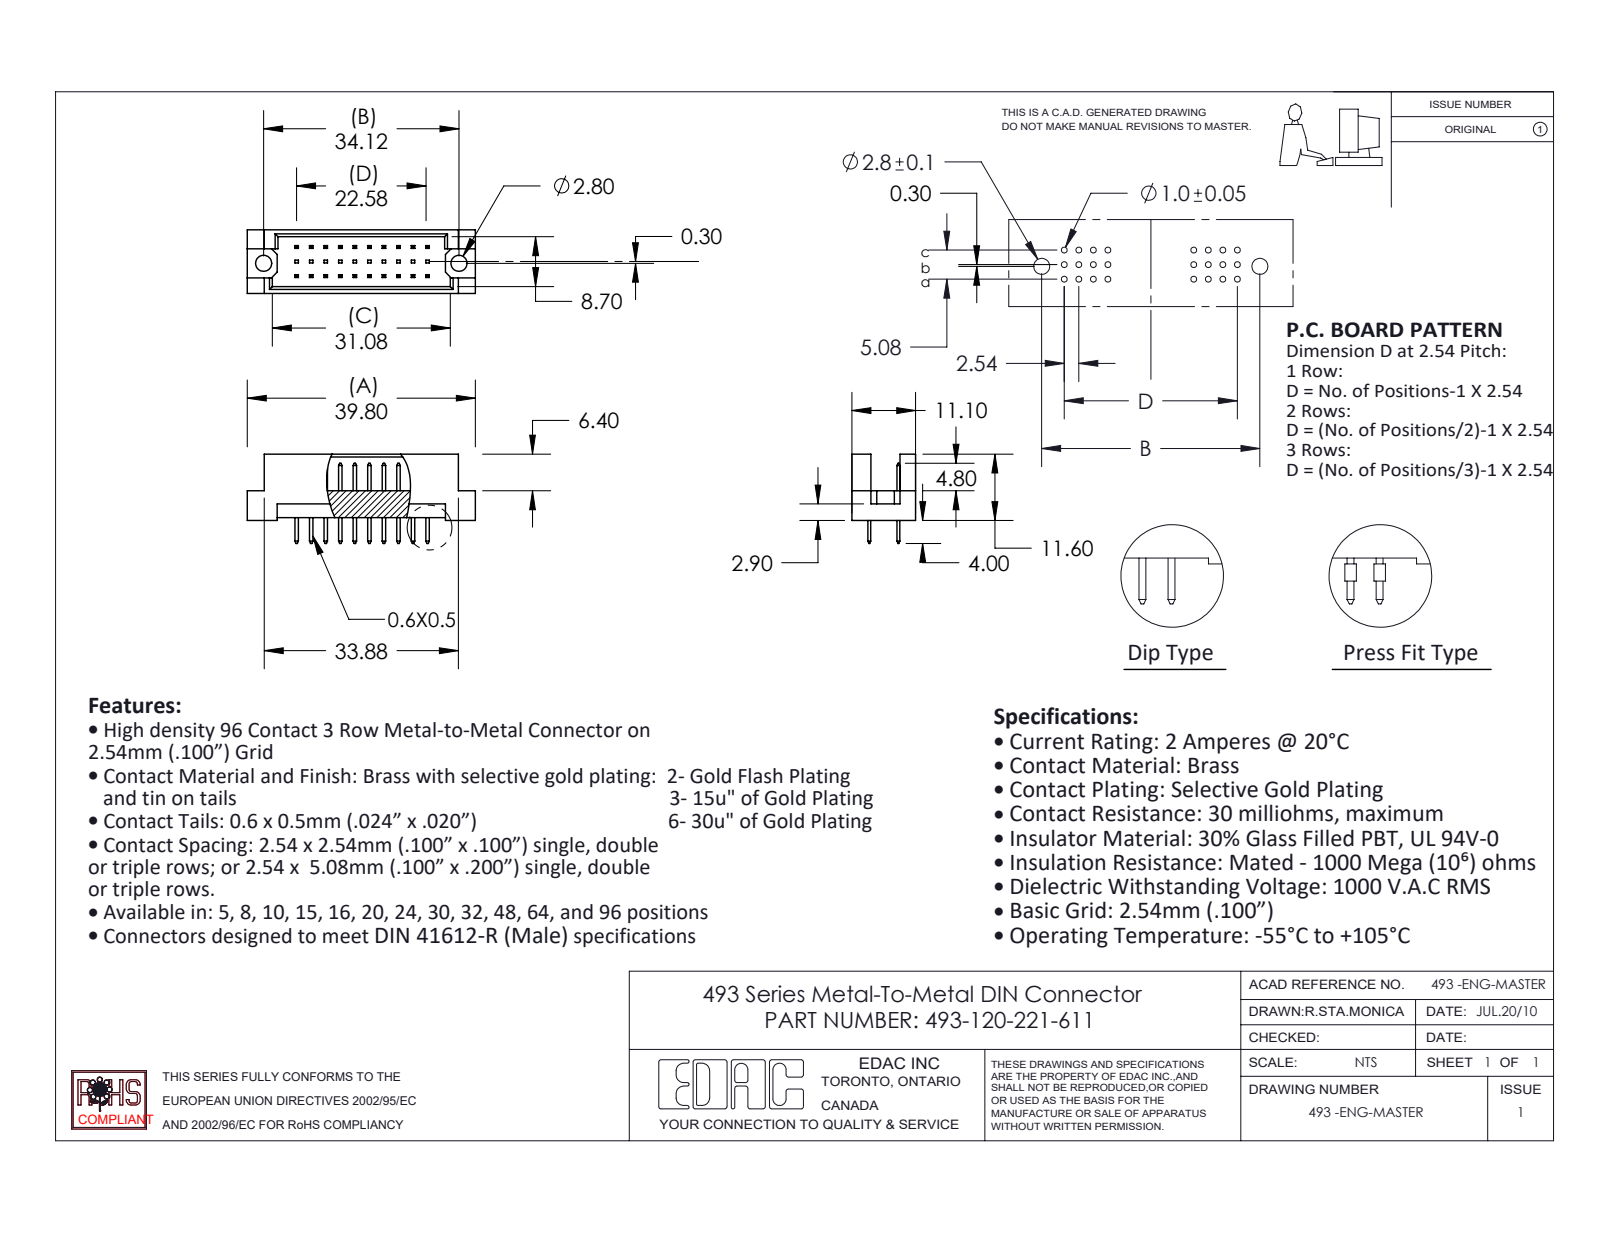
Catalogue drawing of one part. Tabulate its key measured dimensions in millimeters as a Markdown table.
| quantity | value |
| --- | --- |
| part name | 493 Part_30; 493-124-221-321; 493-290_21 |
| STEP written by | SolidWorks 2020 (CONFIG_CONTROL_DESIGN) |
| units | millimeters |
| bodies | 21 solids, 452 faces (448 planar, 4 cylindrical, 0 other) |
| overall size | 39.8 × 15.6 × 11.1 |
| volume | 2 455 mm³ |
| surface area | 3 346 mm² |
| round holes (diameter × count) | 2.8 × 2 |
| main face-to-face distances | 1.2, 9.9, 5.08, 11.1, 2.54, 0.5, 8.7, 4.7, 2.76, 3.26 |
| hole center spacings | 34.12 |
